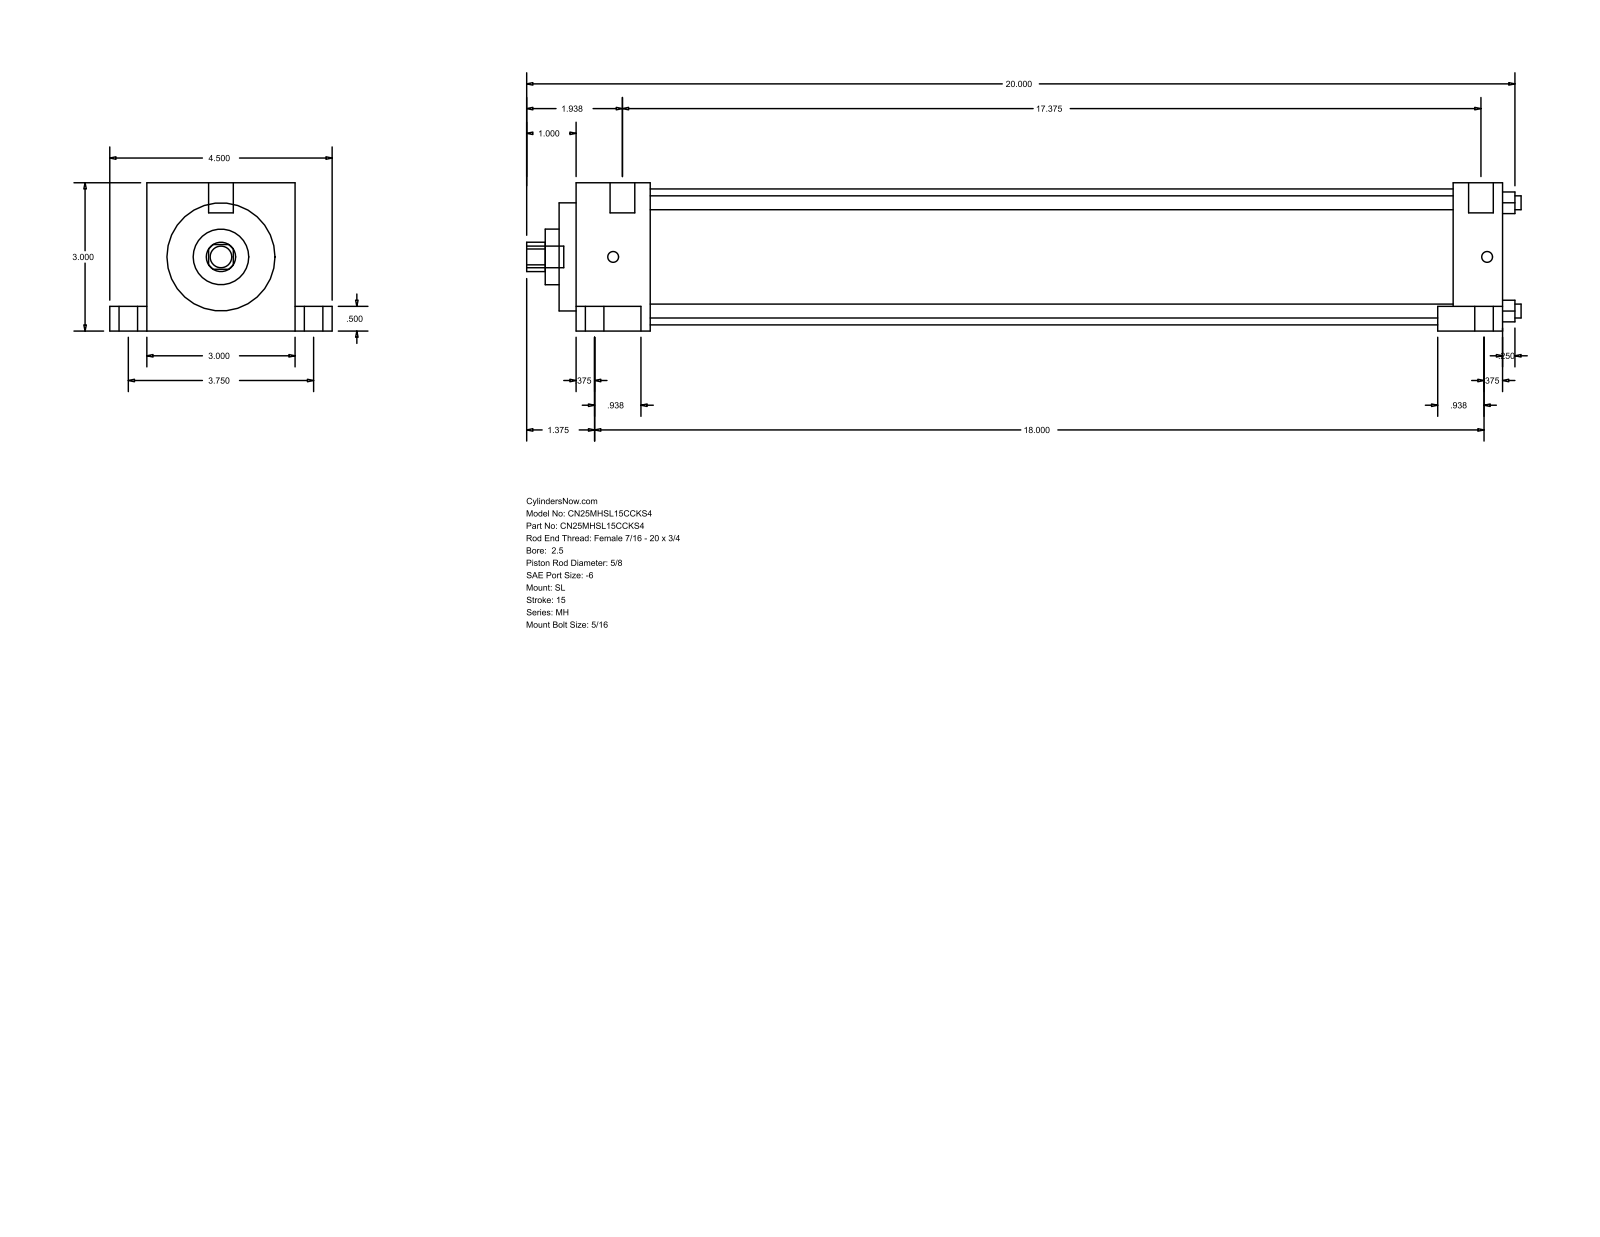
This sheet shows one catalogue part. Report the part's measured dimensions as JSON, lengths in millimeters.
{"part_name": "MH_SL__0250_0.625", "step_written_by": "GSSL Pune (CONFIG_CONTROL_DESIGN)", "units": "millimeters", "bodies": {"solids": 0, "faces": 86, "planar": 61, "cylindrical": 25, "other": 0}, "overall_size": [511.18, 114.3, 76.2], "round_holes": [[7.14, 4], [15.88, 1], [28.57, 1], [55.55, 1], [69.85, 1]], "round_bosses_or_shafts": [[15.88, 2], [9.53, 2], [5.56, 2], [12.7, 1], [11.11, 1]], "partial_cylinders_radius": [[7.54, 1]], "face_to_face_distances": [76.2, 25.4, 459.58, 484.98, 12.7, 63.5, 19.05, 95.25, 31.75, 451.64], "hole_center_spacings": [39.33, 55.62, 78.66]}
